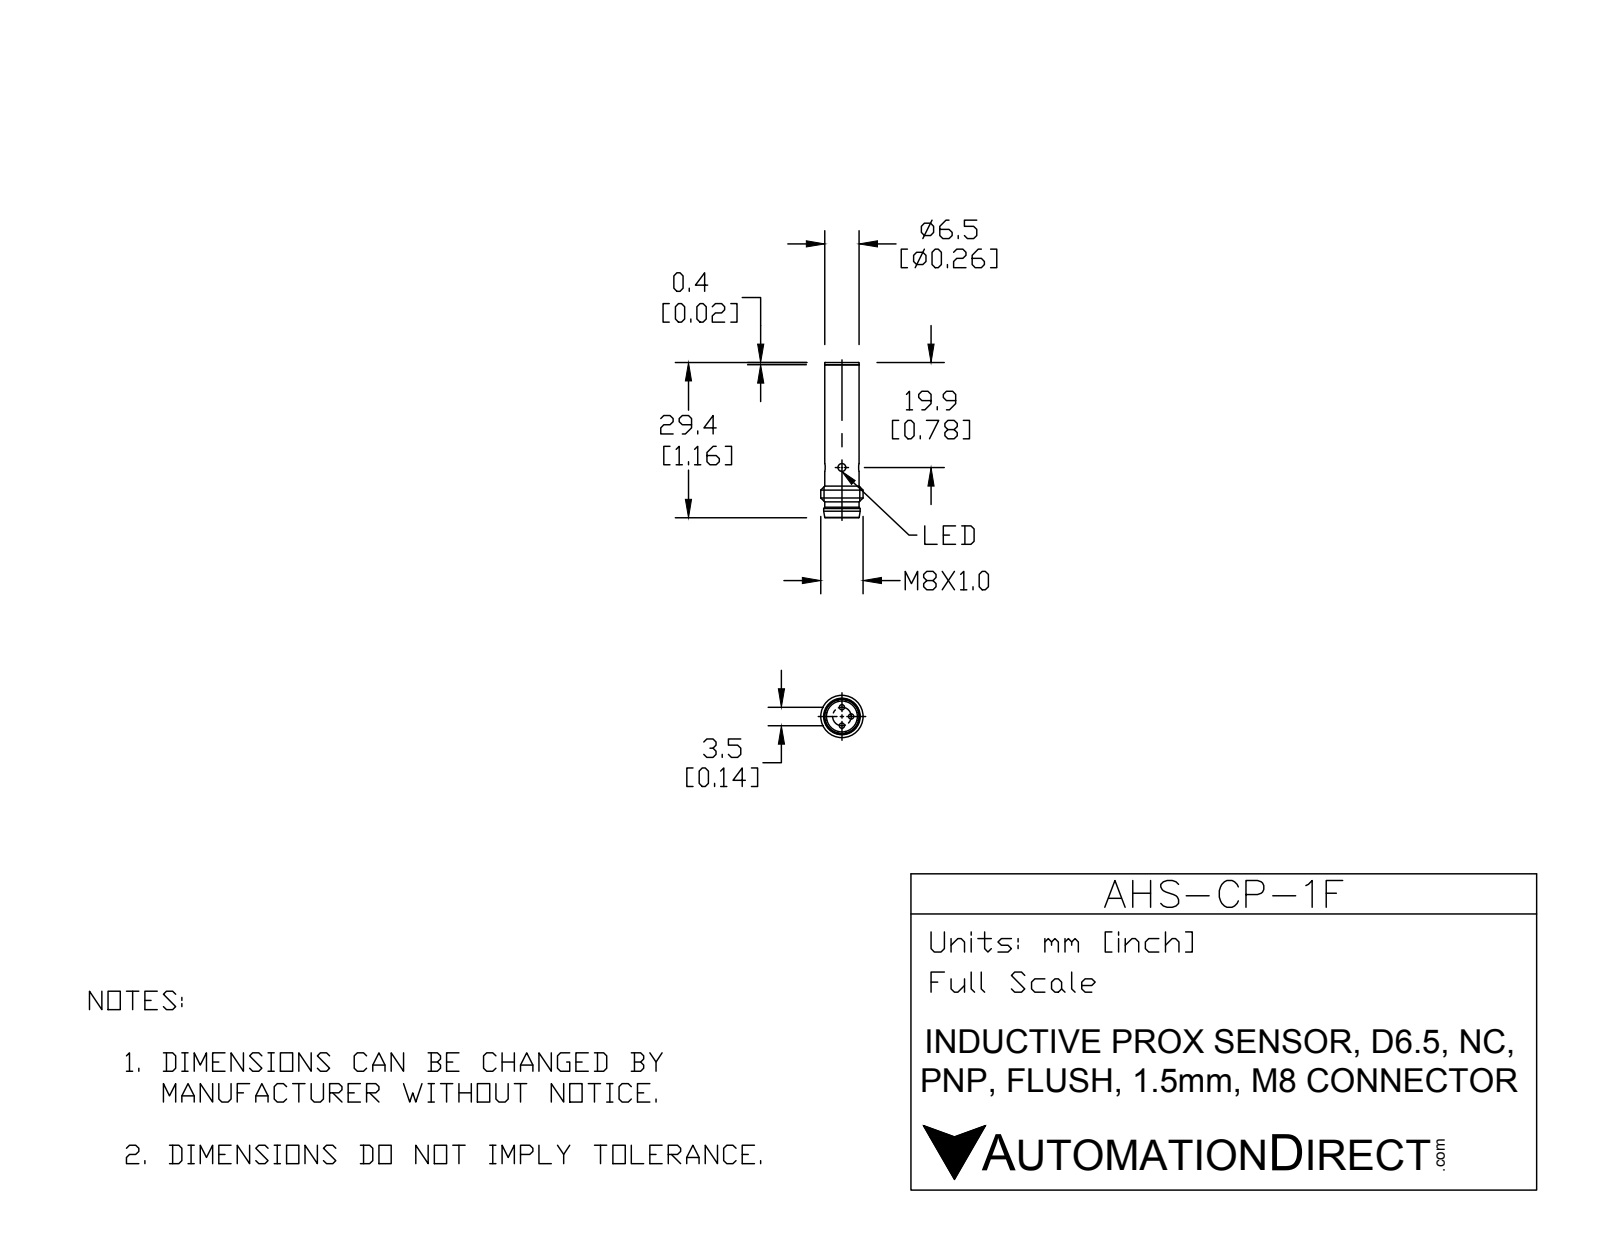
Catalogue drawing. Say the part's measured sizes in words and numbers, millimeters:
The part is named "AHS-CP-1F". Its 3-D file was written by "SolidWorks 2015 (CONFIG_CONTROL_DESIGN)". It is 4 solids with 56 faces: 12 planar, 26 cylindrical and 18 other. Overall it measures 29.4 by 8 by 8 millimeters. Its volume is 891 cubic millimeters and its surface area 842 square millimeters. Round holes: 2 of diameter 1.5, 1 of diameter 5.85. Round bosses or shafts: 3 of diameter 1, 1 of diameter 8, 1 of diameter 6.9, 1 of diameter 6.5. The main face-to-face distances are 24.4, 3, 27.4, 5.5, 2, 5, 29.4, 29, 27, 24.
